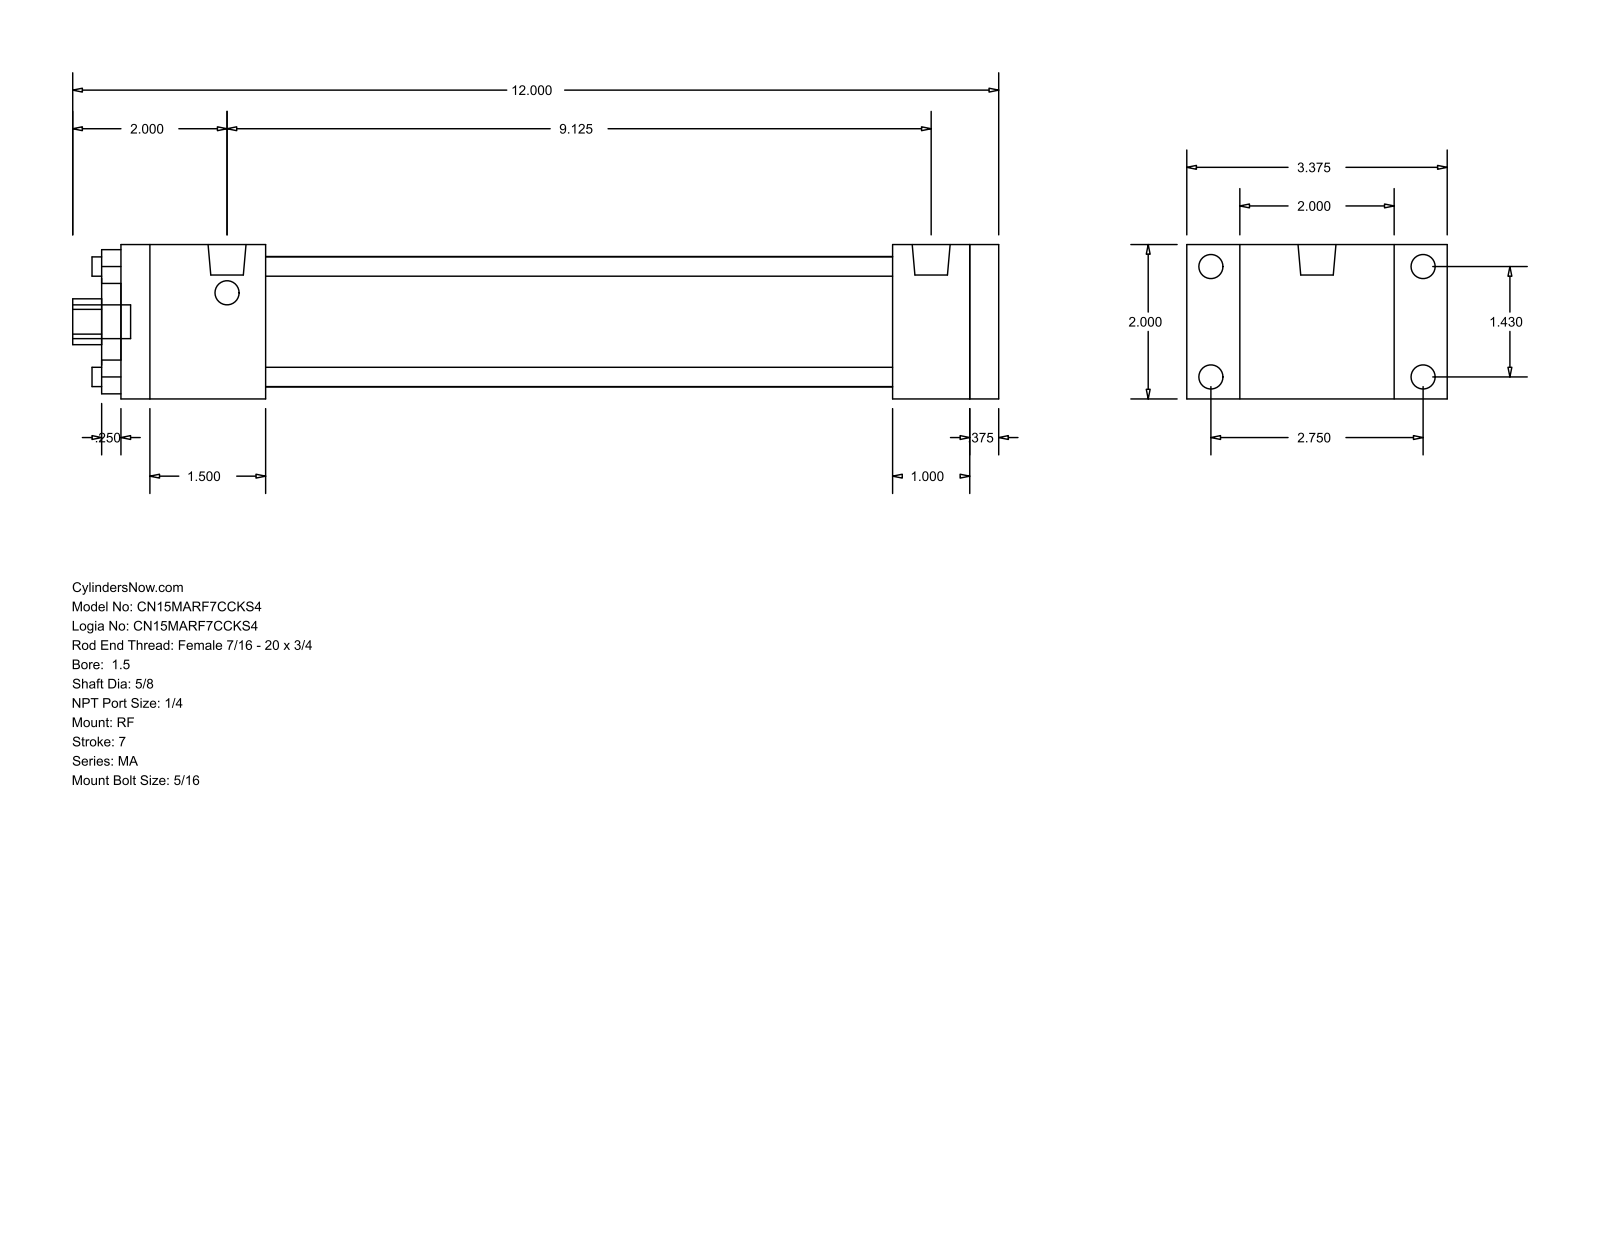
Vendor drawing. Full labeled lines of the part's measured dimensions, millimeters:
Part name (STEP PRODUCT): MA_RF__0150_0.625
STEP written by: GSSL Pune (CONFIG_CONTROL_DESIGN)
Units: millimetres
Bodies: 0 solids, 92 faces (64 planar, 28 cylindrical, 0 other)
Overall size (bounding box): 304.8 × 85.72 × 50.8
Round holes (diameter × count): ⌀6.35 ×4, ⌀15.88 ×1, ⌀28.57 ×1, ⌀42.93 ×1
Round bosses / shafts (diameter × count): ⌀7.94 ×8, ⌀12.49 ×2, ⌀11.11 ×1
Partial cylindrical surfaces — rounded edges, fillets, slot ends (radius × count): R7.54 ×1
Main face-to-face distances: 50.8, 9.53, 288.92, 279.39, 254, 25.39, 34.92, 47.62, 206.38, 231.77
Hole centre spacings: 25.68, 36.32, 51.36
